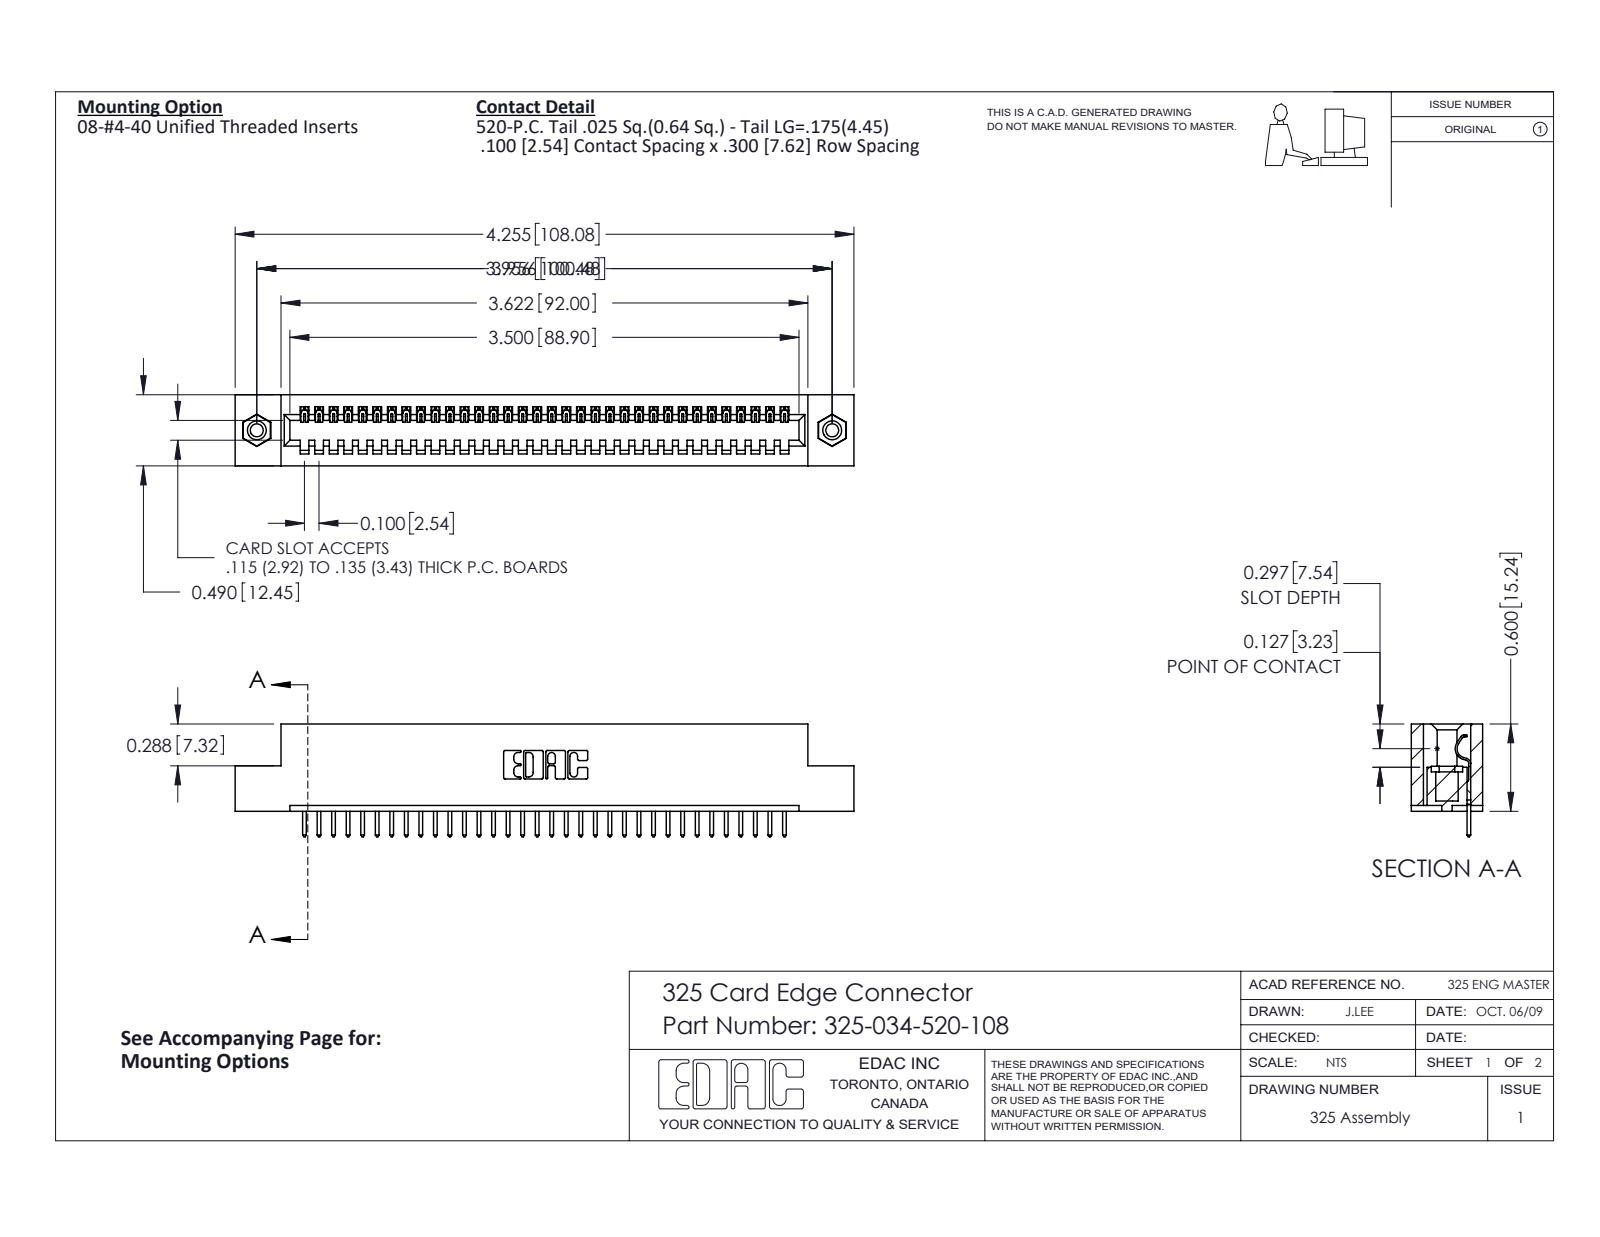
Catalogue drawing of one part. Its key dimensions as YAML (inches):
part_name: "325-034-520-108; 325-292-001_325-293-120; 345-250-001_345-250-003-102; 325 Part_TI"
step_written_by: "SolidWorks 2016 (CONFIG_CONTROL_DESIGN)"
units: inches
bodies: {solids: 37, faces: 2146, planar: 1530, cylindrical: 600, other: 16}
overall_size: [4.255, 0.775, 0.49]
volume: 0.828
surface_area: 22.23
round_holes:
  - {diameter: 0.089, count: 2}
  - {diameter: 0.125, count: 2}
  - {diameter: 0.16, count: 2}
round_bosses_or_shafts:
  - {diameter: 0.155, count: 2}
partial_cylinders:
  - {radius: 0.006, count: 68}
  - {radius: 0.01, count: 68}
  - {radius: 0.01, count: 22}
  - {radius: 0.007, count: 6}
  - {radius: 0.031, count: 6}
  - {radius: 0.026, count: 3}
  - {radius: 0.014, count: 1}
  - {radius: 0.022, count: 1}
face_to_face_distances: [0.083, 0.407, 0.49, 0.3, 0.107, 0.383, 0.025, 0.325, 0.04, 0.56]
hole_center_spacings: [3.956]
